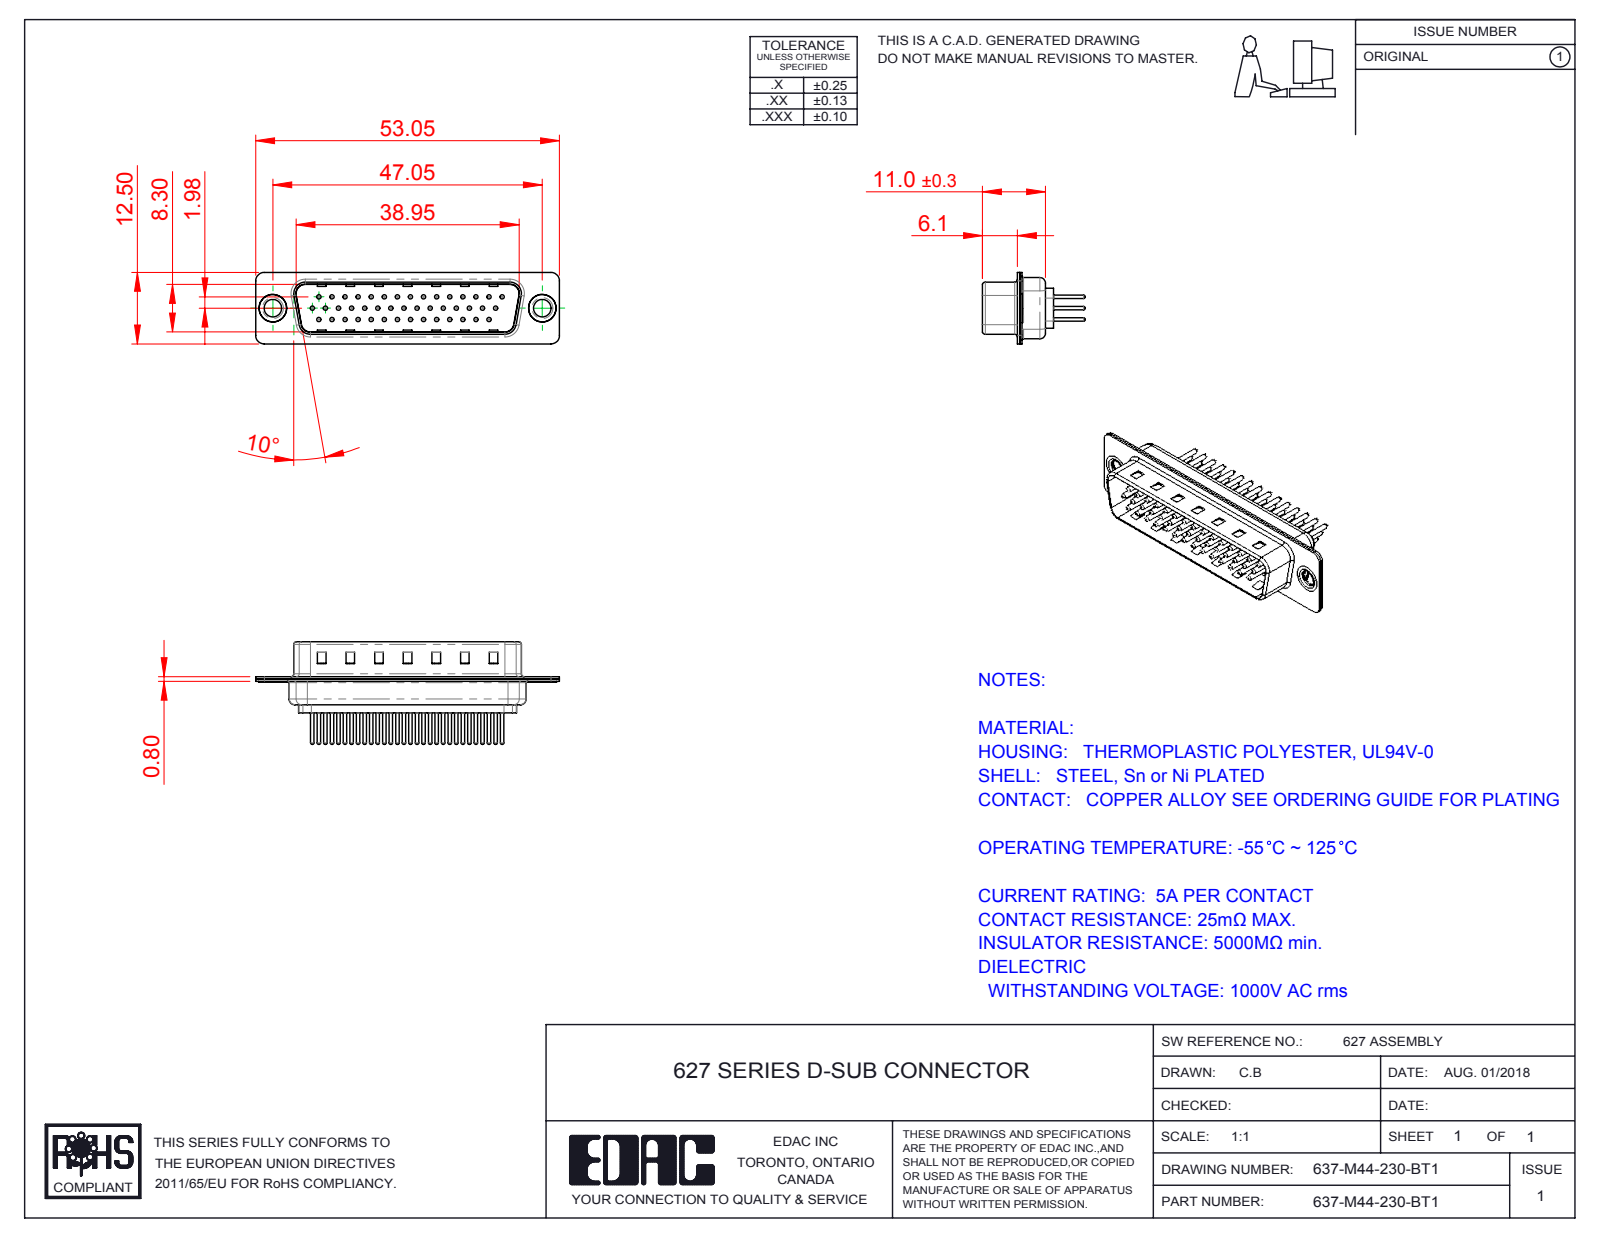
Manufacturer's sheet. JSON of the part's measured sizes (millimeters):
{"part_name": "637M Shell Rear_44 Contacts; 637-M44-230-BT1; 637M Shell Front_44 Contacts; 637M Contact Row 1_30 (+4 more)", "step_written_by": "SolidWorks 2016 (CONFIG_CONTROL_DESIGN)", "units": "millimeters", "bodies": {"solids": 49, "faces": 1978, "planar": 479, "cylindrical": 737, "other": 762}, "overall_size": [53.05, 17.9, 12.5], "volume_mm3": 2750, "surface_area_mm2": 8321, "round_holes": [[0.75, 44], [1.6, 44], [2, 44], [3.05, 2], [4, 2], [4.8, 2]], "round_bosses_or_shafts": [[1.5, 44], [0.6, 44], [2, 3], [0.75, 3], [5, 2], [4.9, 2], [3.55, 2]], "partial_cylinders_radius": [[1.5, 16], [2, 12], [0.5, 8], [1.6, 8], [0.25, 4], [0.6, 4], [0.65, 4], [0.9, 4]], "face_to_face_distances": [0.4, 0.8, 9.5, 9.1, 8.7, 9.9, 0.75, 1.1, 0.35, 5.9], "hole_center_spacings": [2.28, 3.96, 2.29, 4.57, 8.24, 6.86, 11.43, 14.99]}
